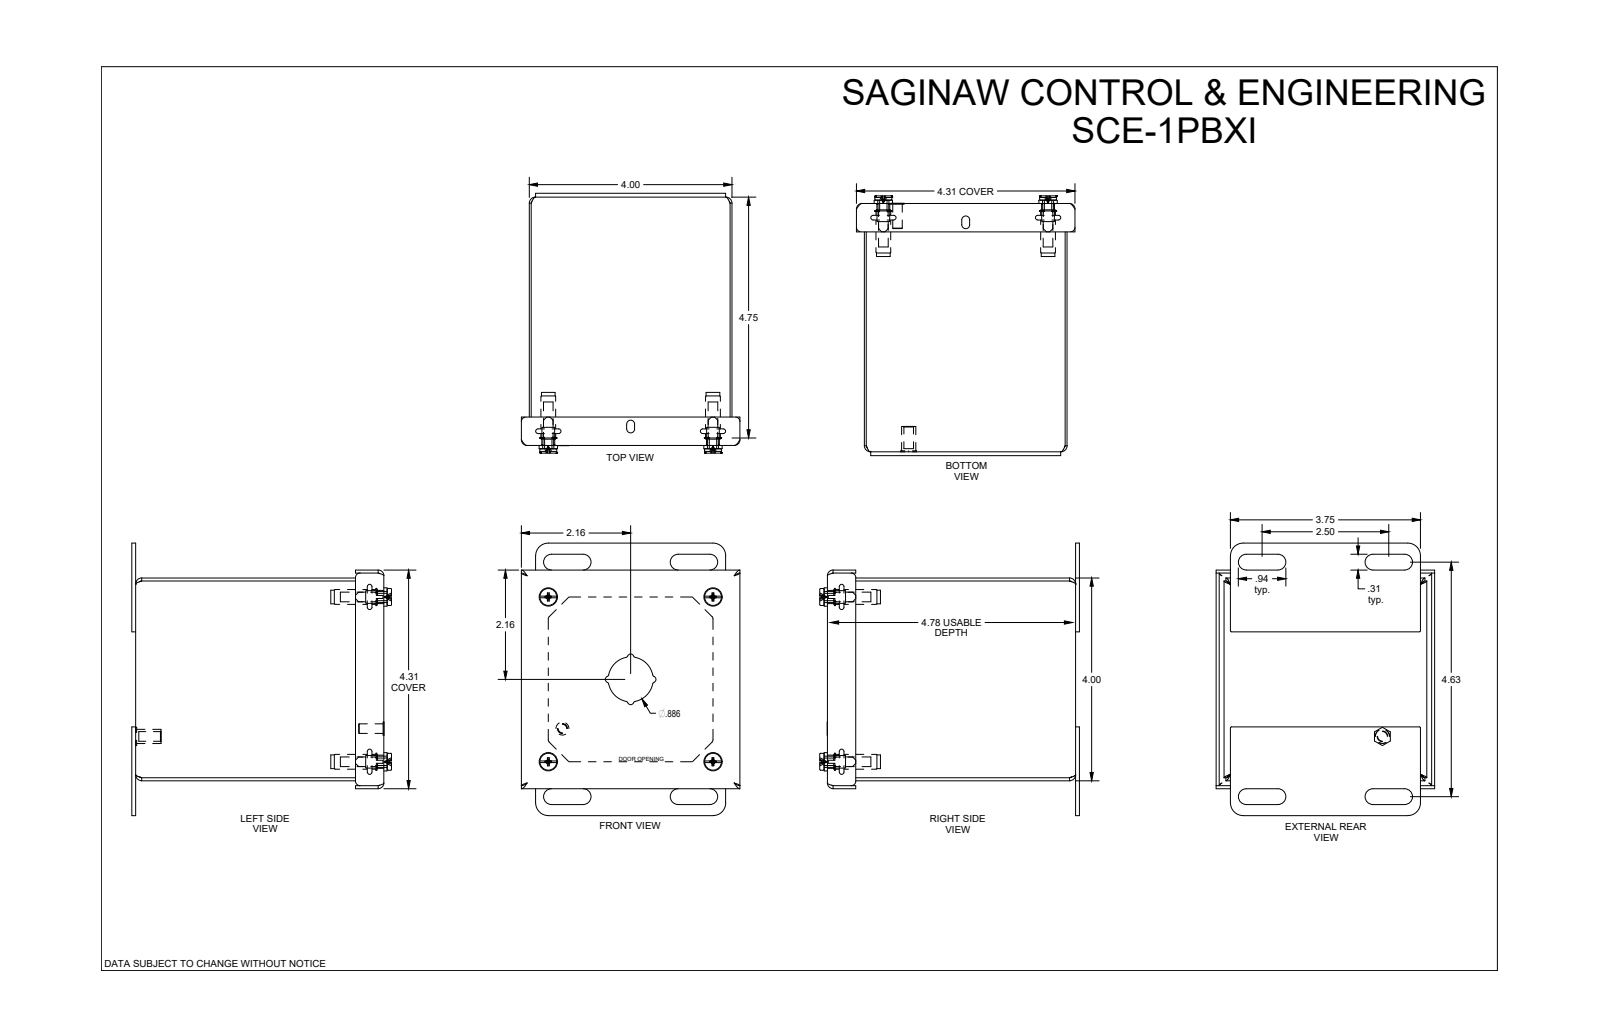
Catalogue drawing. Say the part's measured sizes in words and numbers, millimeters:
The part is named "SCE-1PBXI". Its 3-D file was written by "SolidWorks 2021 (AUTOMOTIVE_DESIGN)". It is 15 solids with 433 faces: 162 planar, 195 cylindrical and 76 other. Overall it measures 136.5 by 127.9 by 109.5 millimeters. Its volume is 141 100 cubic millimeters and its surface area 184 500 square millimeters. Round holes: 5 of diameter 4.8, 4 of diameter 5.6, 4 of diameter 6.4, 4 of diameter 6.8, 4 of diameter 8.1. Round bosses or shafts: 4 of diameter 9.2, 4 of diameter 8.6, 4 of diameter 7.4, 4 of diameter 6.9, 4 of diameter 6.6, 1 of diameter 7.1, 1 of diameter 6.5, 1 of diameter 4.8. Partial cylindrical surfaces (rounded edges, fillets, slot ends): 20 of radius 1.5, 8 of radius 0.4, 8 of radius 1, 8 of radius 2.9, 8 of radius 4, 8 of radius 6.2, 4 of radius 0.5, 4 of radius 1.6. The main face-to-face distances are 1.5, 100.1, 101.6, 98.6, 122.9, 124.4, 121.4, 1.9, 3.4, 124.8. The hole center spacings are 82.6, 82.6, 116.7, 71, 82.4, 98.8, 116.7, 17.8.
